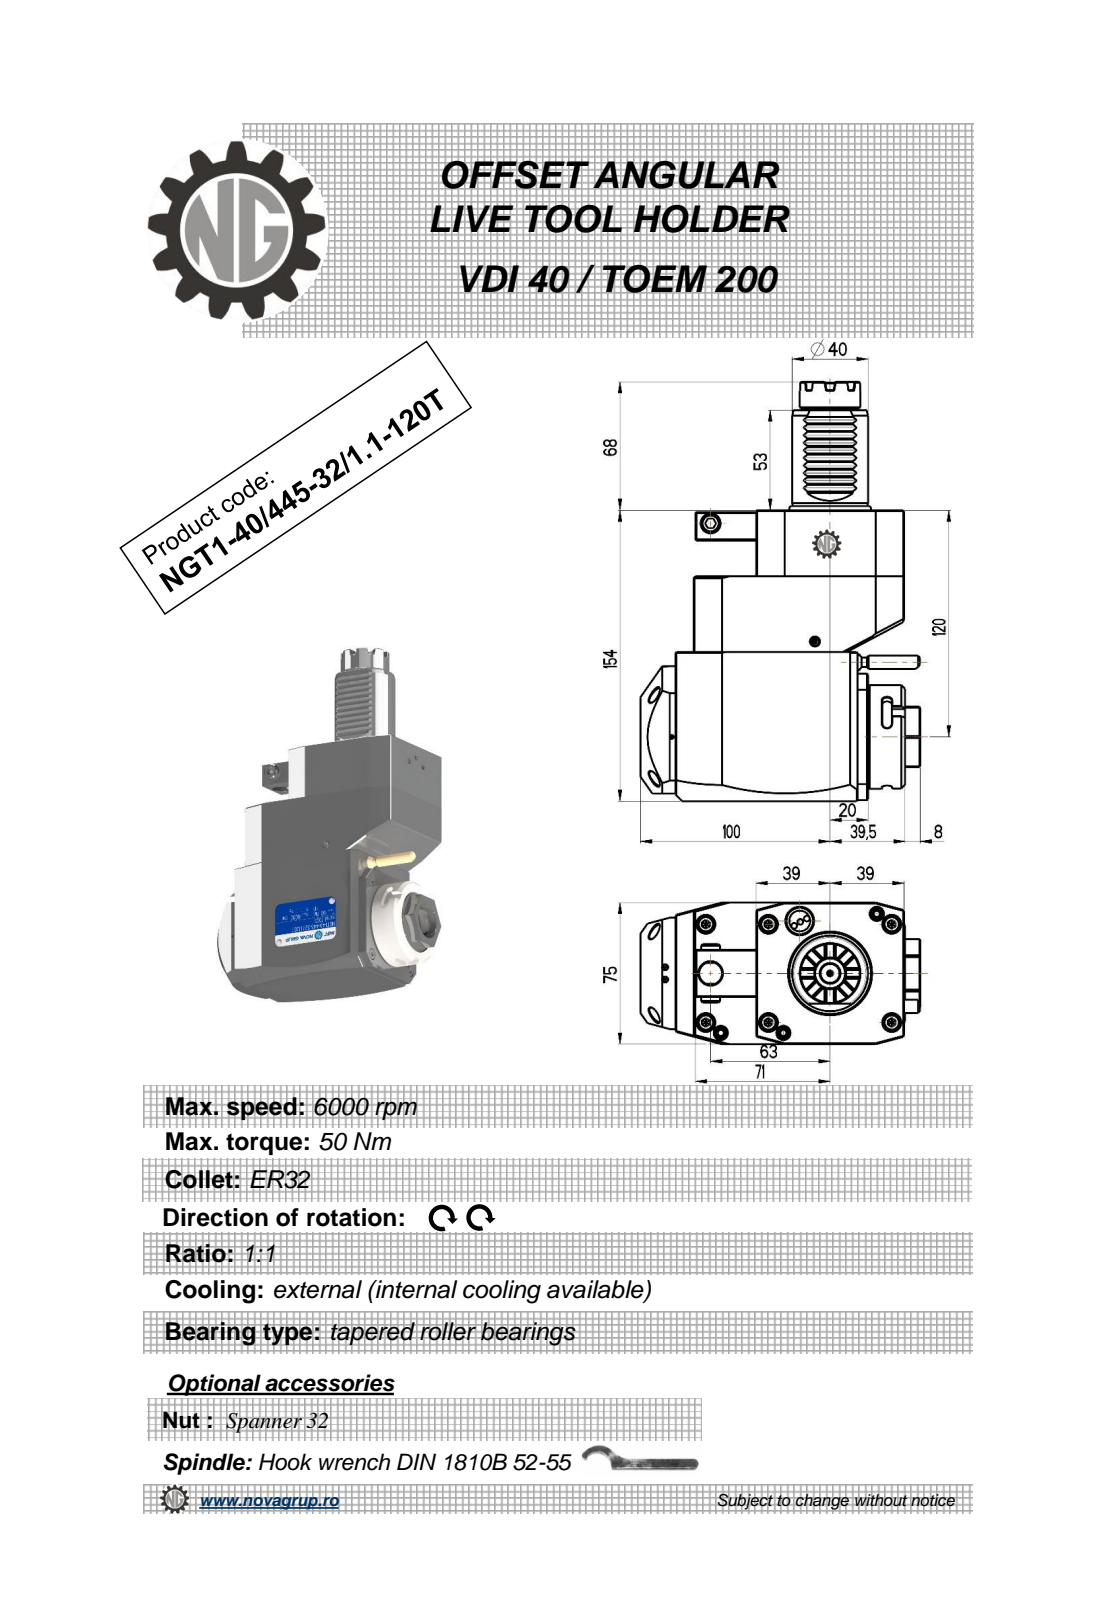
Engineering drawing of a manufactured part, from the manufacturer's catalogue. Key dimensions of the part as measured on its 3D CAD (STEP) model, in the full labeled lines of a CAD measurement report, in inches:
Part name (STEP PRODUCT): NGT1_40_445_32_1_1_120T
STEP written by: PRO/ENGINEER BY PARAMETRIC TECHNOLOGY CORPORATION, 2010280 (CONFIG_CONTROL_DESIGN)
Units: inches
Bodies: 1 solid, 411 faces (231 planar, 72 cylindrical, 108 other)
Overall size (bounding box): 8.74 × 5.807 × 2.953
Volume: 77.62 in³ · Surface area: 140.2 in²
Round holes (diameter × count): ⌀0.098 ×1, ⌀0.118 ×1, ⌀0.335 ×1, ⌀0.374 ×1, ⌀0.472 ×1, ⌀0.906 ×1
Round bosses / shafts (diameter × count): ⌀0.353 ×2, ⌀2.165 ×1, ⌀1.89 ×1, ⌀1.575 ×1, ⌀1.26 ×1, ⌀0.661 ×1, ⌀0.394 ×1, ⌀0.276 ×1
Partial cylindrical surfaces — rounded edges, fillets, slot ends (radius × count): R0.012 ×10, R0.098 ×6, R7.087 ×2, R0.02 ×1, R0.339 ×1, R0.965 ×1, R1.476 ×1
Main face-to-face distances: 2.953, 6.063, 0.748, 2.323, 4.37, 1.378, 3.622, 4.685, 0.02, 1.299
Hole centre spacings: 1.701, 2.956, 4.429
